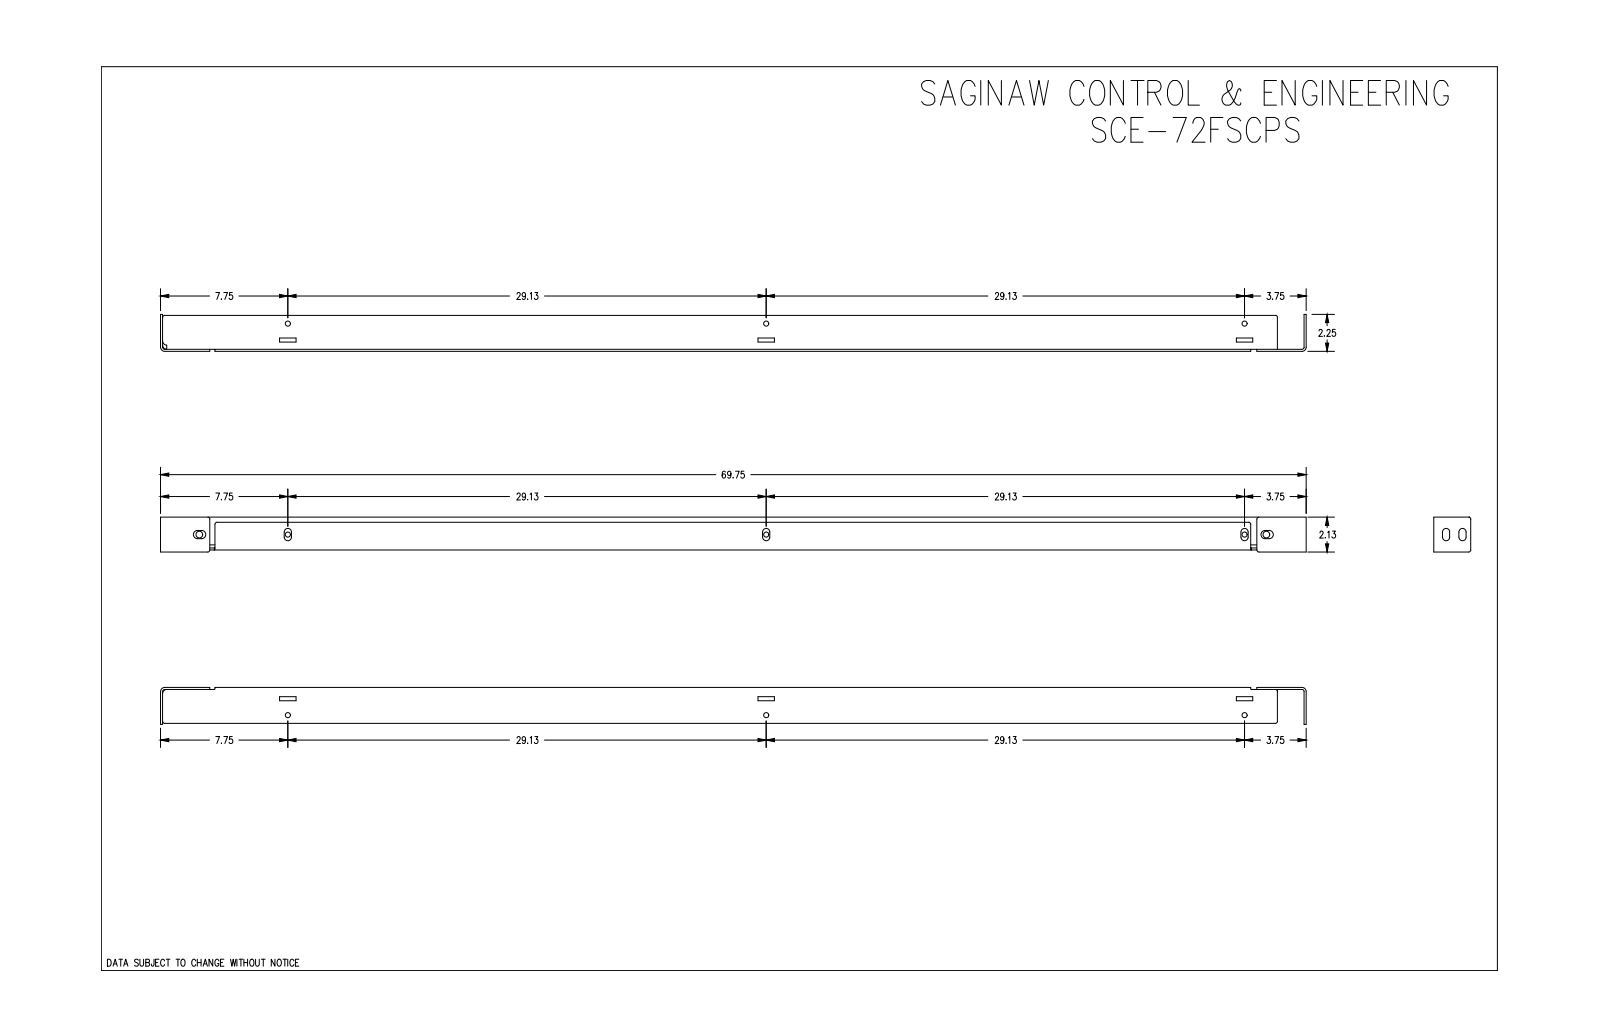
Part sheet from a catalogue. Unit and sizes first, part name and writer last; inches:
Units: inches
Overall size (bounding box): 69.75 × 2.25 × 2.125
Round holes (diameter × count): ⌀0.312 ×6, ⌀0.406 ×2
Partial cylindrical surfaces — rounded edges, fillets, slot ends (radius × count): R0.125 ×17, R0.25 ×10, R0.219 ×6, R0.219 ×4
Main face-to-face distances: 0.125, 0.125, 2, 1.875, 1.75, 1.875, 0.25, 0.313, 2.187, 2.062
Hole centre spacings: 29.125, 29.125, 58.25, 1.328, 5.39, 30.453, 34.515, 59.578
Volume: 62.22 in³ · Surface area: 1 040 in²
Bodies: 4 solids, 141 faces (79 planar, 56 cylindrical, 6 other)
Part name (STEP PRODUCT): SCE-72FSCPS
STEP written by: SolidWorks 2019 (CONFIG_CONTROL_DESIGN)
